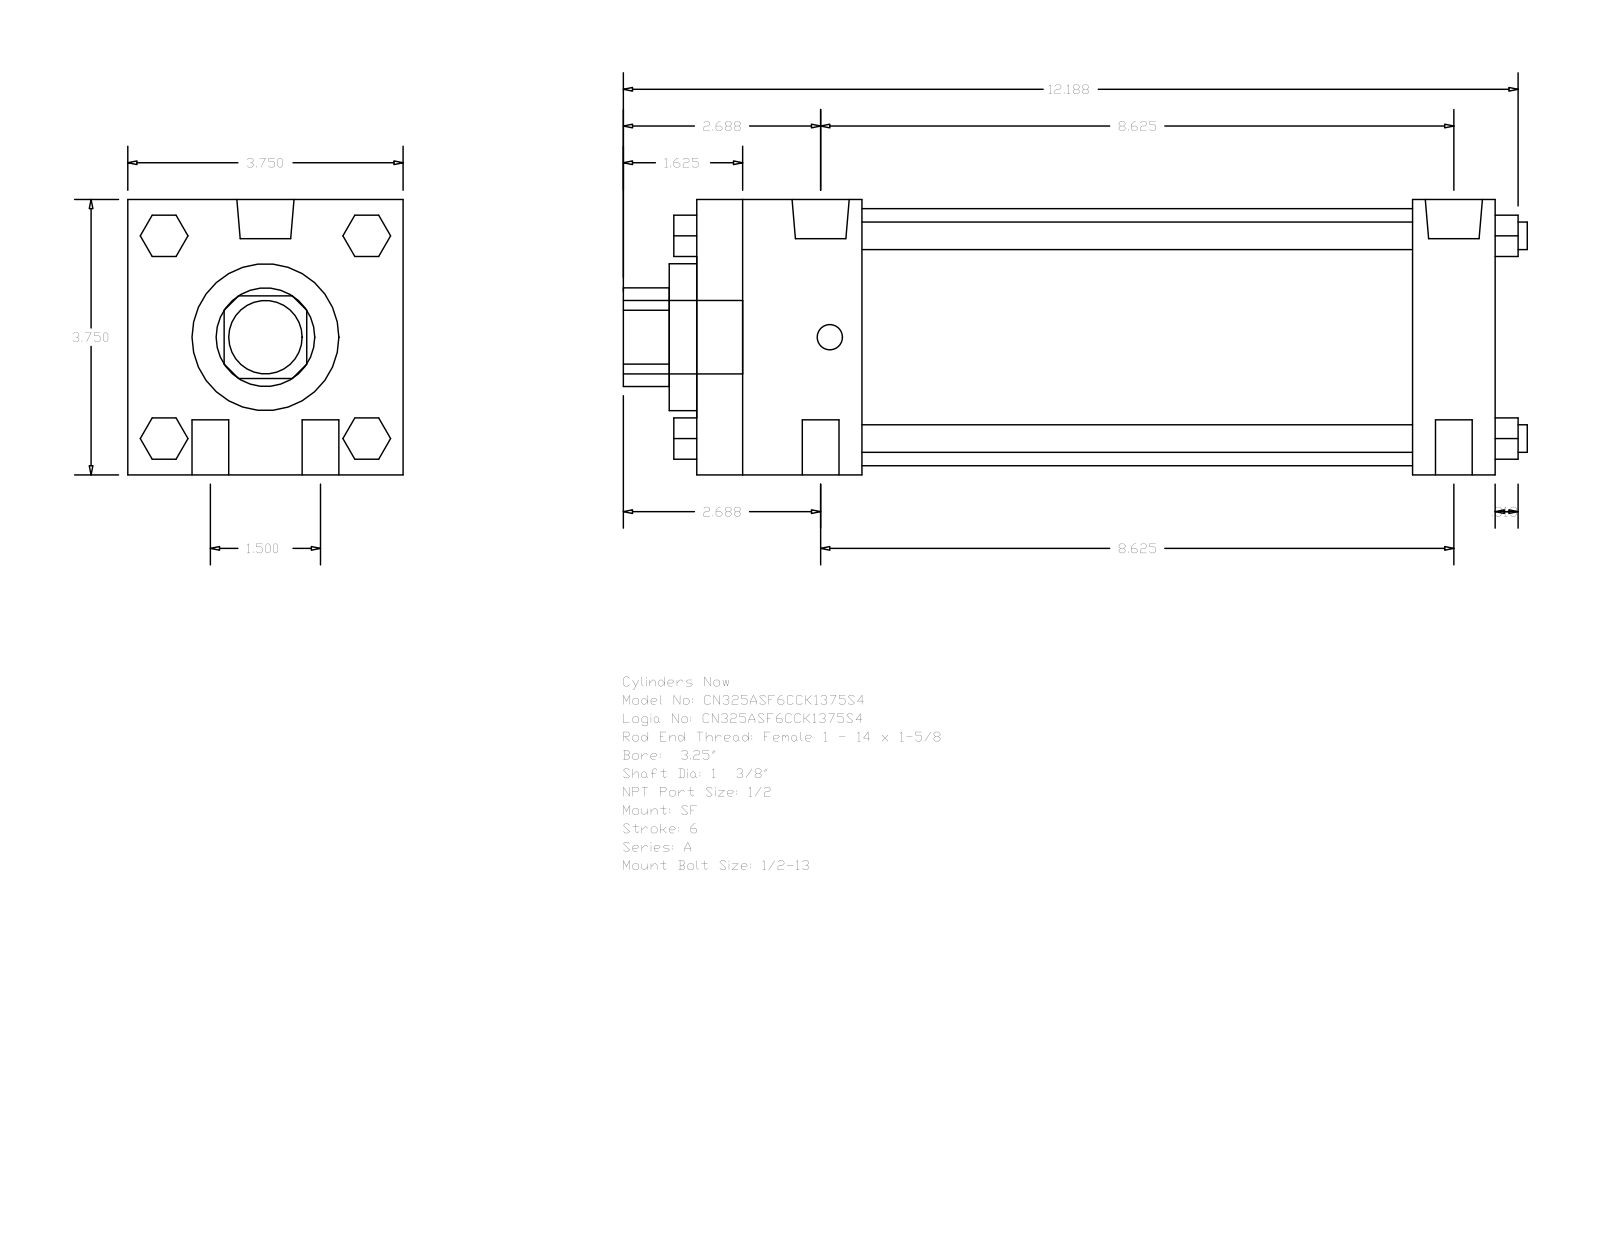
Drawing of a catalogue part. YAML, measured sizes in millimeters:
part_name: "A_SF__0325_1.375"
step_written_by: "GSSL Pune (CONFIG_CONTROL_DESIGN)"
units: millimeters
bodies: {solids: 0, faces: 124, planar: 94, cylindrical: 30, other: 0}
overall_size: [312.74, 95.25, 95.25]
round_holes:
  - {diameter: 34.92, count: 1}
  - {diameter: 50.8, count: 1}
  - {diameter: 88.9, count: 1}
round_bosses_or_shafts:
  - {diameter: 12.7, count: 4}
  - {diameter: 9.53, count: 4}
  - {diameter: 19.77, count: 2}
  - {diameter: 8.73, count: 2}
  - {diameter: 25.4, count: 1}
partial_cylinders:
  - {radius: 17.06, count: 1}
face_to_face_distances: [95.24, 276.22, 28.57, 247.65, 57.15, 190.5, 219.07, 9.52, 66.67, 257.17]
